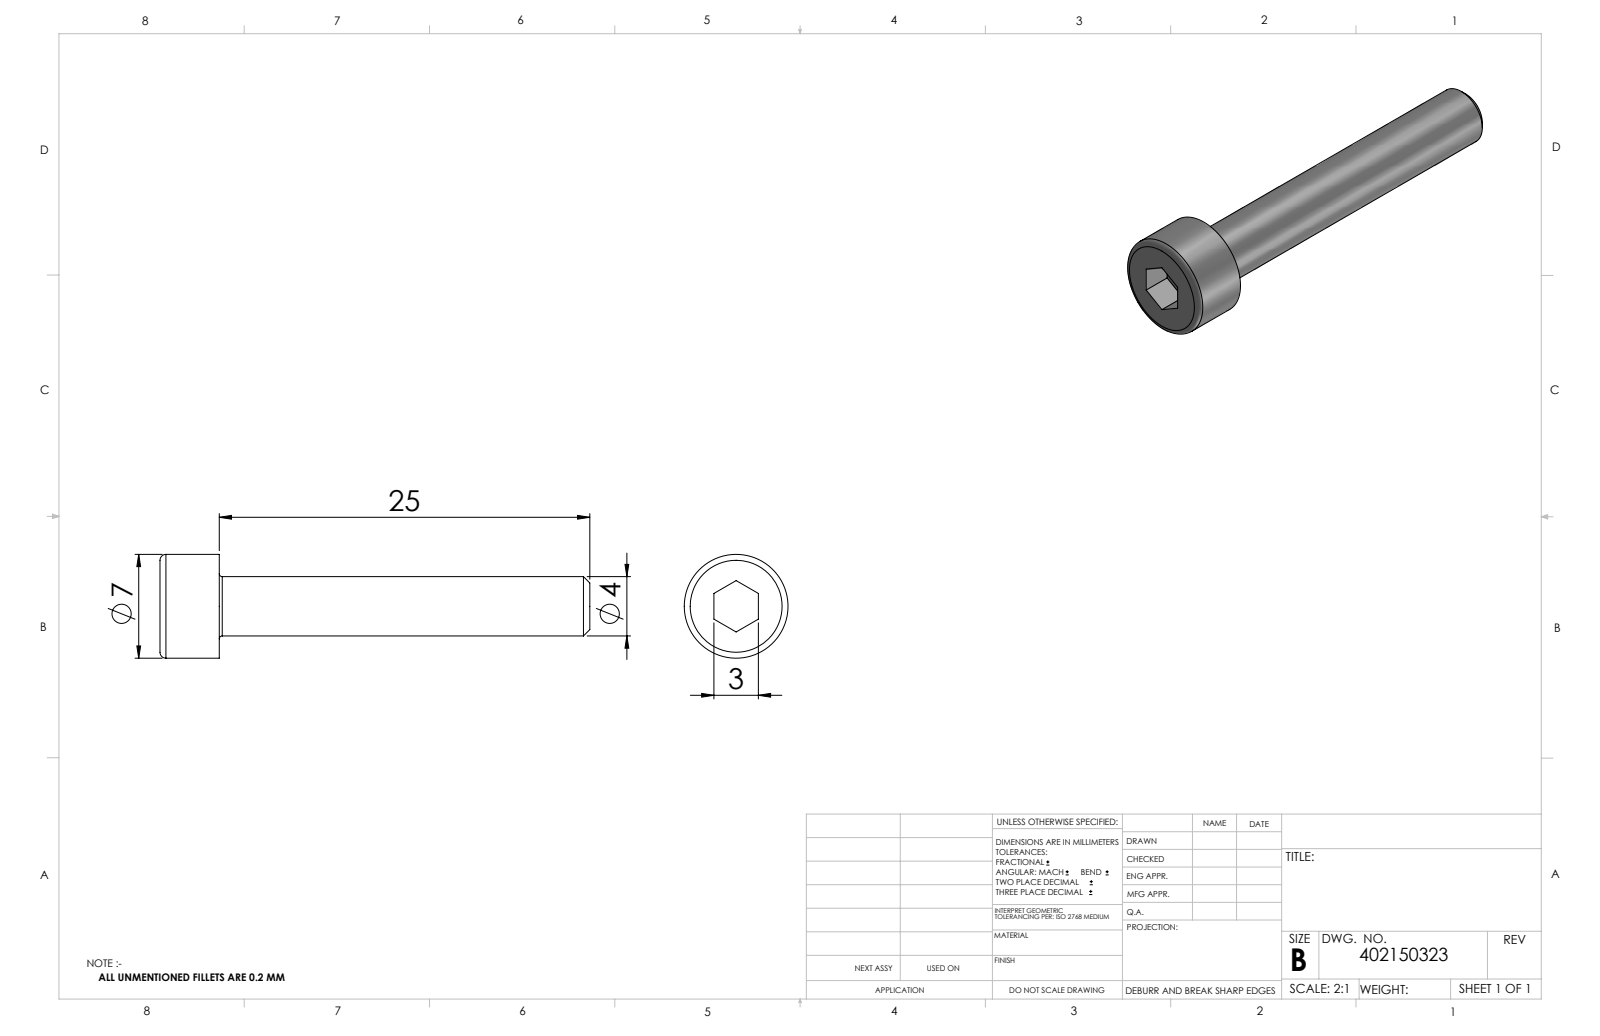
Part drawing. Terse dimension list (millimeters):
name: 402150323_c_1
written by: SolidWorks 2014 (CONFIG_CONTROL_DESIGN)
unit: mm
bodies: 1 solid, 20 faces (10 planar, 4 cylindrical, 6 other)
size: 29 × 7 × 7
volume: 451 mm³; area: 492 mm²
bosses: 1× ⌀7, 1× ⌀4
face distances: 4, 2, 3, 29, 27, 25
